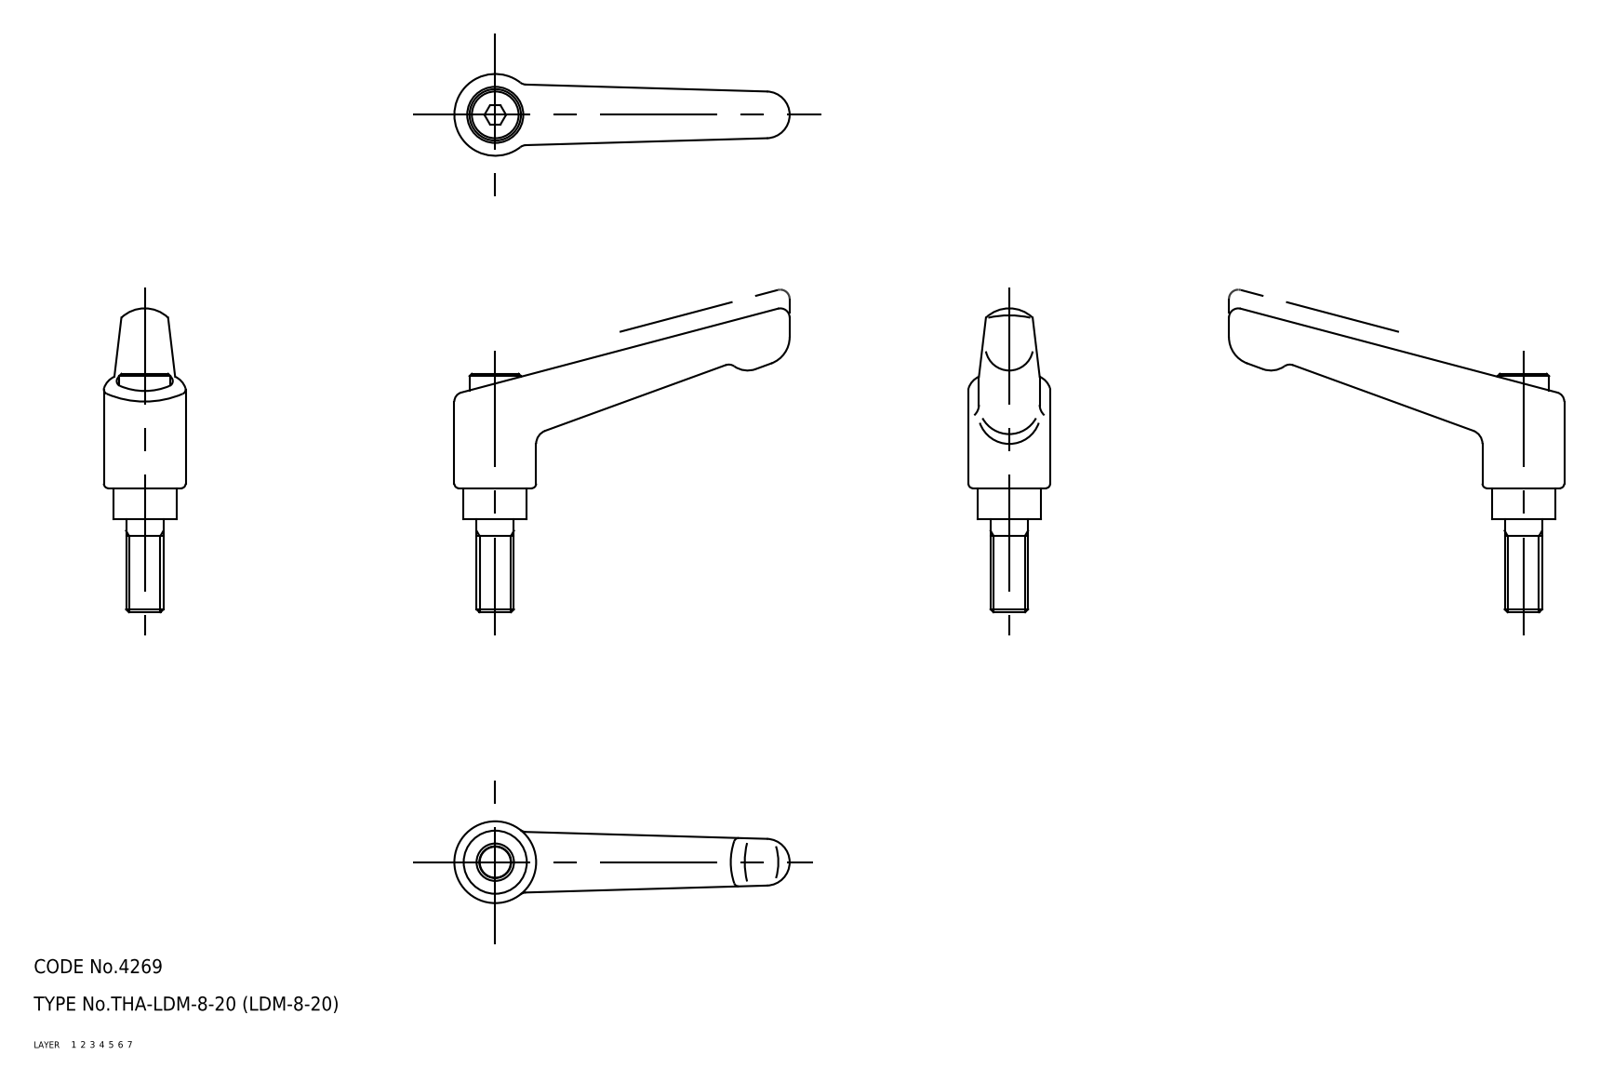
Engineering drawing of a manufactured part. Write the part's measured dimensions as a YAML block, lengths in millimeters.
part_name: "sleeve; screw; handle; LDM_8_20_26306_36"
step_written_by: "CADfix (AUTOMOTIVE_DESIGN)"
units: millimeters
bodies: {solids: 3, faces: 75, planar: 0, cylindrical: 0, other: 75}
overall_size: [71.75, 65, 17.5]
volume: 13114
surface_area: 6518
